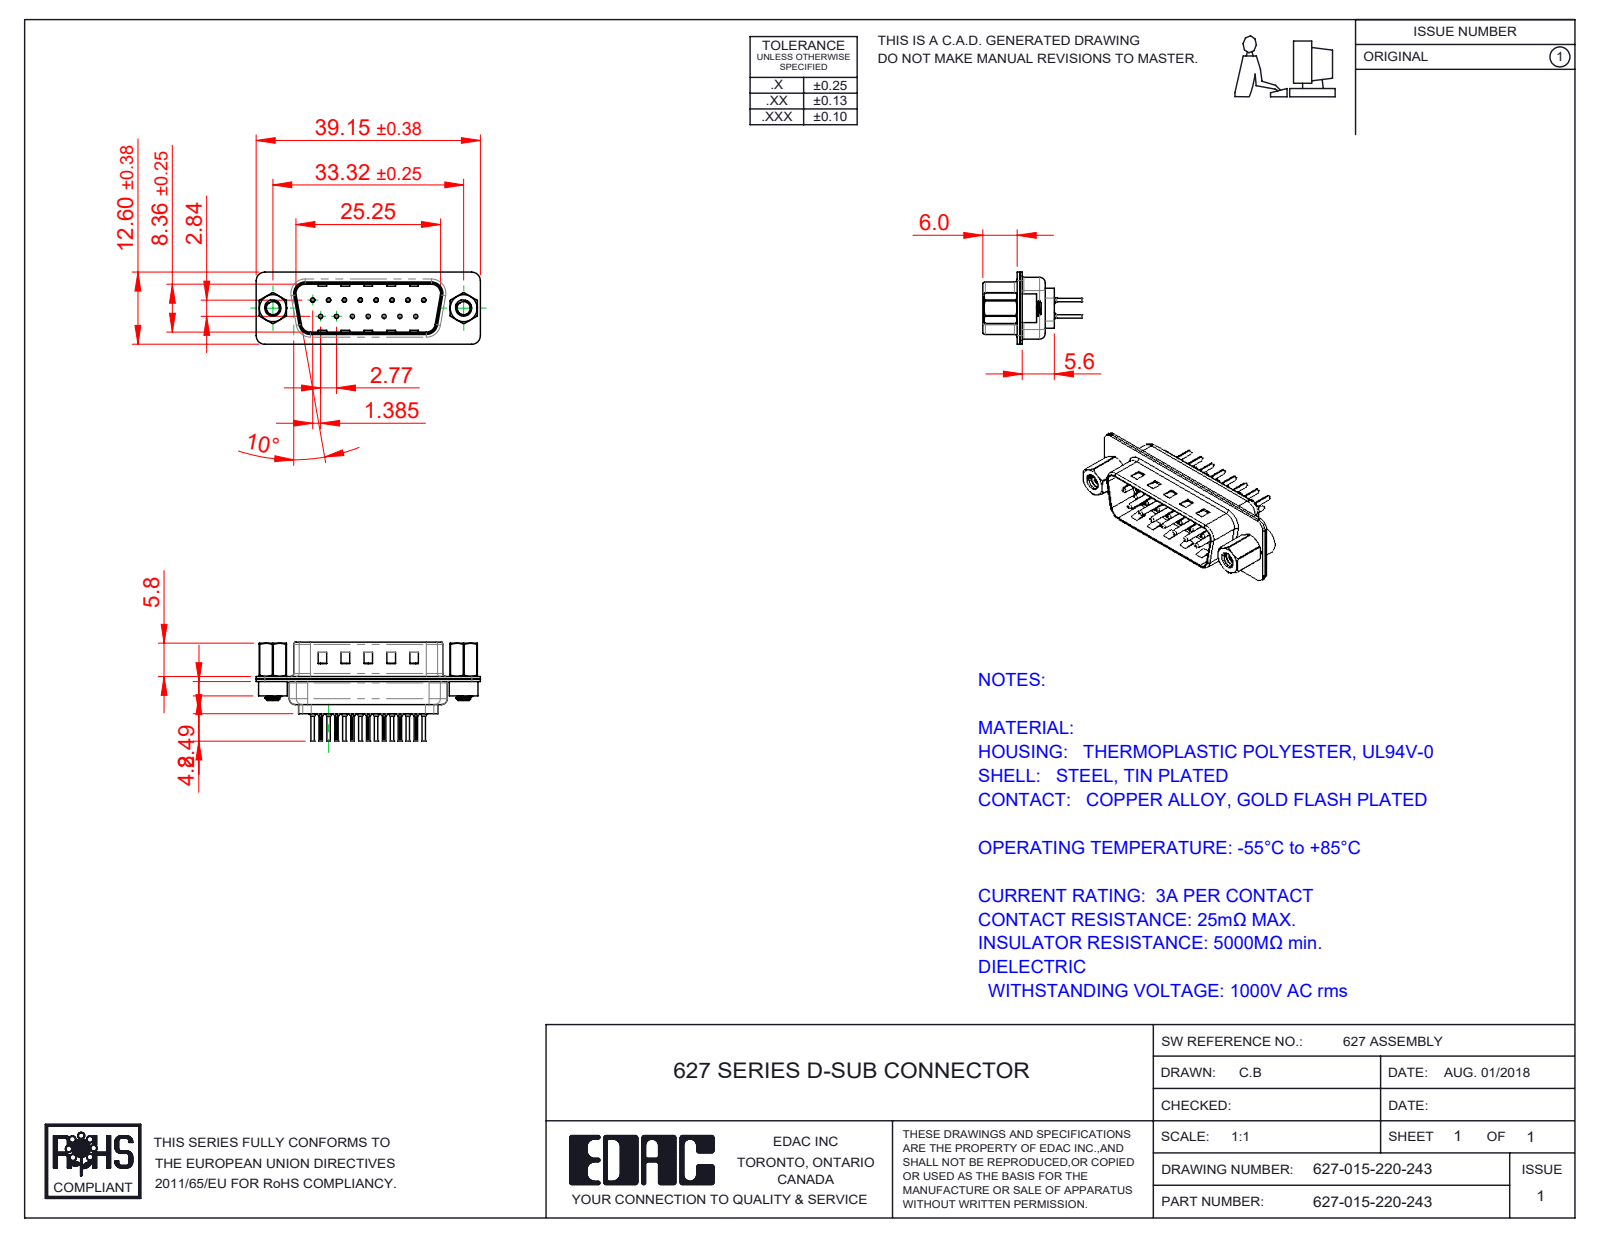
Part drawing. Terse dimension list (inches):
name: 627 4-40 Hex Standoff; 627 4-40 Threaded Rivet; 627 Shell Rear_15 Contacts; 627 Shell Front_15 Contacts (+4 more)
written by: SolidWorks 2020 (CONFIG_CONTROL_DESIGN)
unit: in
bodies: 22 solids, 1932 faces (521 planar, 758 cylindrical, 653 other)
size: 1.541 × 0.681 × 0.496
volume: 0.124 in³; area: 9.089 in²
holes: 15× ⌀0.008, 15× ⌀0.014, 15× ⌀0.043, 15× ⌀0.063, 2× ⌀0.089, 2× ⌀0.09, 2× ⌀0.157, 2× ⌀0.189
bosses: 15× ⌀0.079, 15× ⌀0.059, 15× ⌀0.03, 15× ⌀0.024, 2× ⌀0.197, 2× ⌀0.193, 2× ⌀0.11
rounds: 30× R0.004, 16× R0.059, 12× R0.079, 8× R0.02, 8× R0.063, 4× R0.01, 4× R0.024, 4× R0.026
face distances: 0.016, 0.018, 0.035, 0.032, 0.377, 0.345, 0.059, 0.055, 0.256, 0.22
hole spacings: 0.124, 0.109, 0.218, 0.327, 0.436, 0.198, 0.198, 0.294
